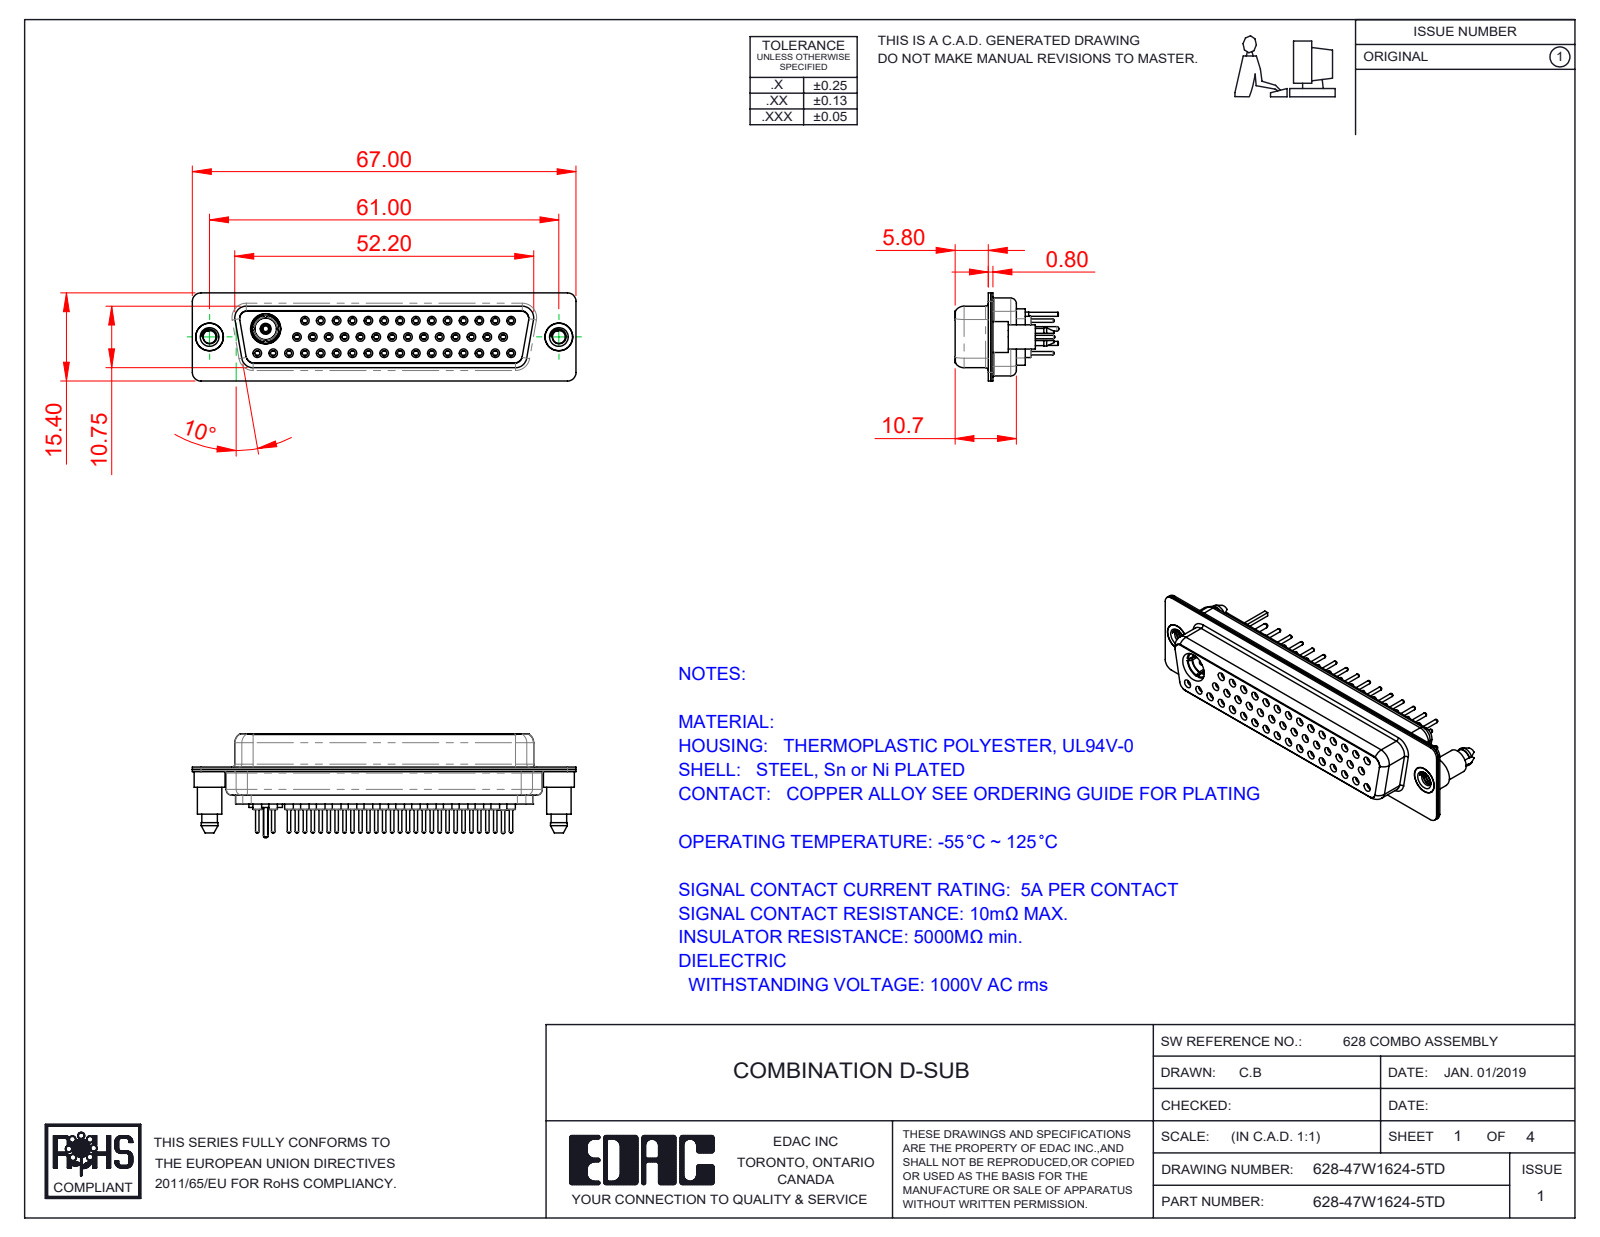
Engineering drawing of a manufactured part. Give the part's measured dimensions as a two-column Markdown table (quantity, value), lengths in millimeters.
| quantity | value |
| --- | --- |
| part name | 628Combo Housing_47W1; 628-47W1624-5TD; 628Combo Shell Rear_50 Contacts; Co-Ax Plug Assy_St (+8 more) |
| STEP written by | SolidWorks 2016 (CONFIG_CONTROL_DESIGN) |
| units | millimeters |
| bodies | 55 solids, 2989 faces (827 planar, 1096 cylindrical, 1066 other) |
| overall size | 67 × 18.15 × 15.4 |
| volume | 7 180 mm³ |
| surface area | 15 219 mm² |
| round holes (diameter × count) | 1.1 × 47, 1.5 × 46, 0.9 × 45, 2 × 45, 1.6 × 31, 1.7 × 14, 4.85 × 3, 2.26 × 2, 4 × 2, 4.05 × 2, 2.83 × 1, 3.3 × 1 |
| round bosses / shafts (diameter × count) | 2.2 × 46, 0.6 × 46, 1.6 × 15, 5.4 × 2, 4.95 × 2, 4.8 × 2, 4.25 × 2, 5.85 × 1 |
| partial cylindrical surfaces (radius × count) | 1.5 × 18, 1.35 × 12, 2 × 12, 1.6 × 10, 0.25 × 4, 0.5 × 4, 0.6 × 4, 0.65 × 4 |
| main face-to-face distances | 0.4, 6.05, 6.45, 11.33, 1.87, 12.25, 6.2, 5.8, 10.35, 10.93 |
| hole center spacings | 3.16, 2.77, 5.54, 8.31, 11.08, 13.85, 16.62, 19.39 |
